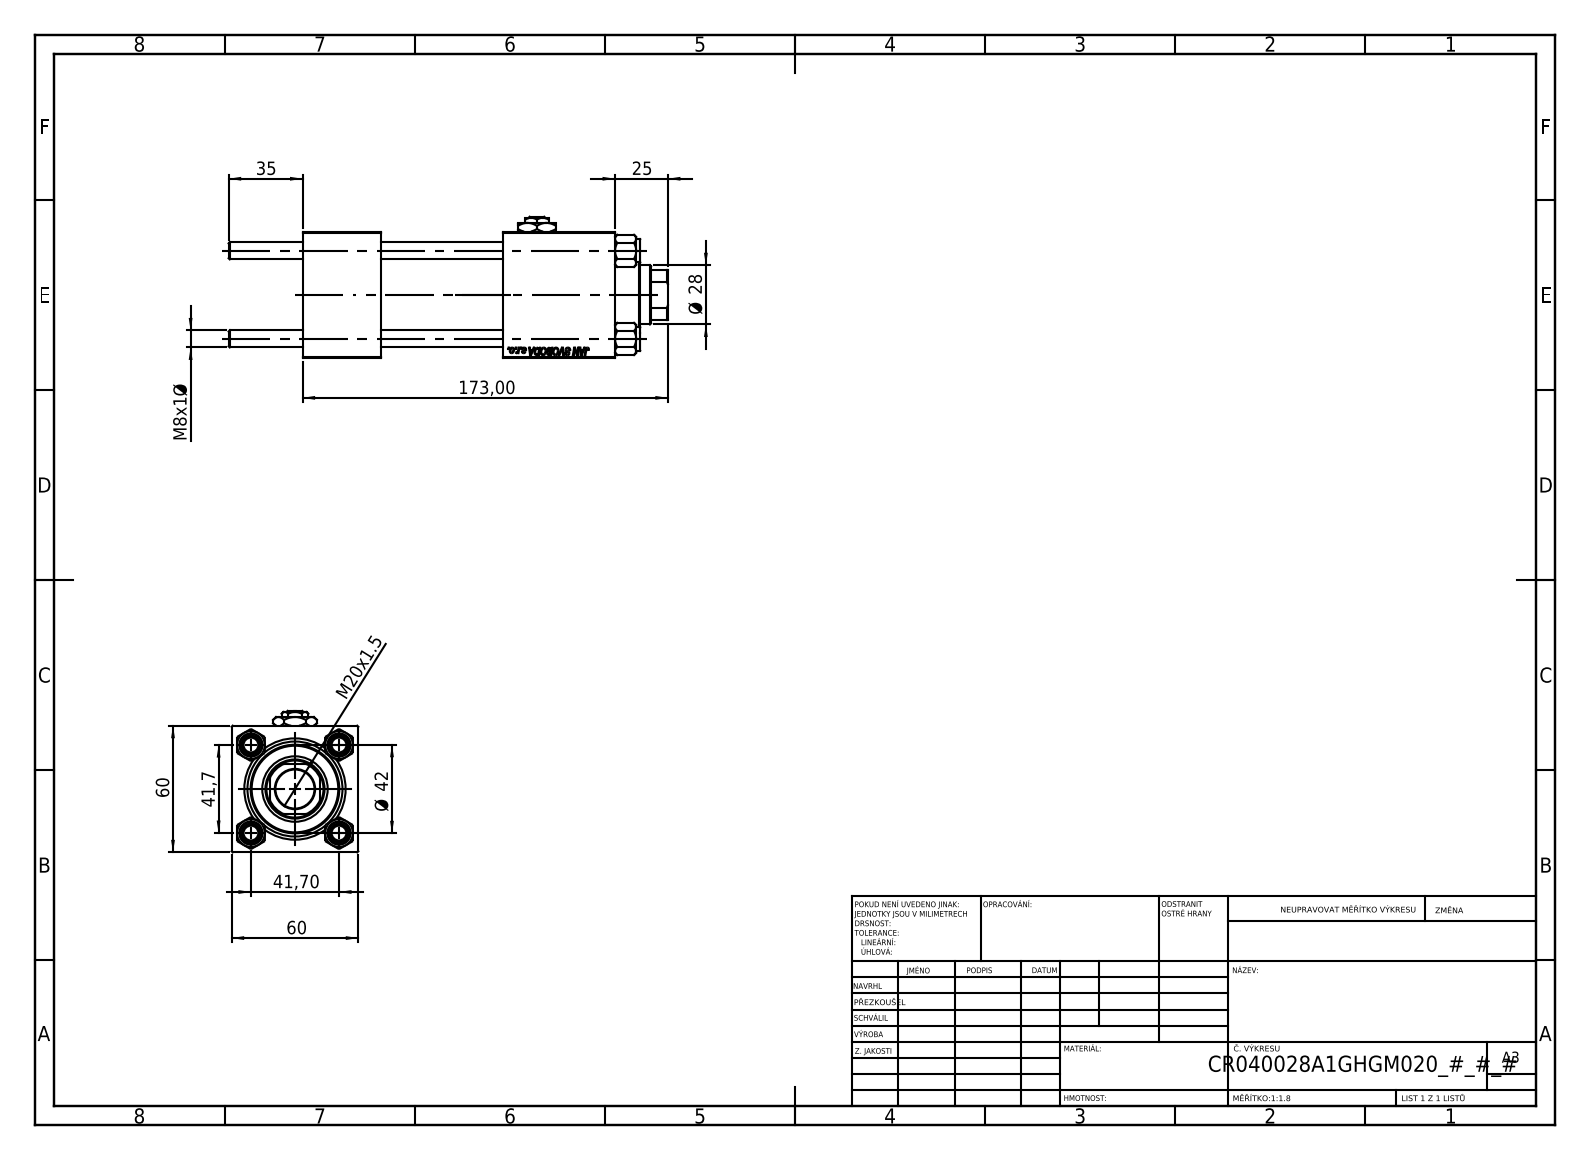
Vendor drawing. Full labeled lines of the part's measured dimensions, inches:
Part name (STEP PRODUCT): NUT_M5; V215_VC_A; V215CR_BODY_A; CR025_012_A_0_G_A_G_M_020_+#_##_TYCINKA (+2 more)
STEP written by: SolidWorks 2019 (CONFIG_CONTROL_DESIGN)
Units: inches
Bodies: 12 solids, 1183 faces (545 planar, 82 cylindrical, 556 other)
Overall size (bounding box): 8.189 × 2.638 × 2.362
Volume: 26.46 in³ · Surface area: 188.1 in²
Round holes (diameter × count): ⌀0.315 ×4, ⌀0.276 ×2, ⌀0.656 ×2, ⌀0.945 ×2, ⌀0.728 ×1, ⌀1.102 ×1, ⌀1.22 ×1, ⌀1.575 ×1, ⌀1.772 ×1
Round bosses / shafts (diameter × count): ⌀0.433 ×4, ⌀1.811 ×1, ⌀1.654 ×1
Partial cylindrical surfaces — rounded edges, fillets, slot ends (radius × count): R0.531 ×1
Main face-to-face distances: 2.362, 1.457, 2.283, 3.74, 2.087, 5.827, 4.37, 4.697, 3.24, 0.957
Hole centre spacings: 1.161, 1.642, 2.322, 3.642
